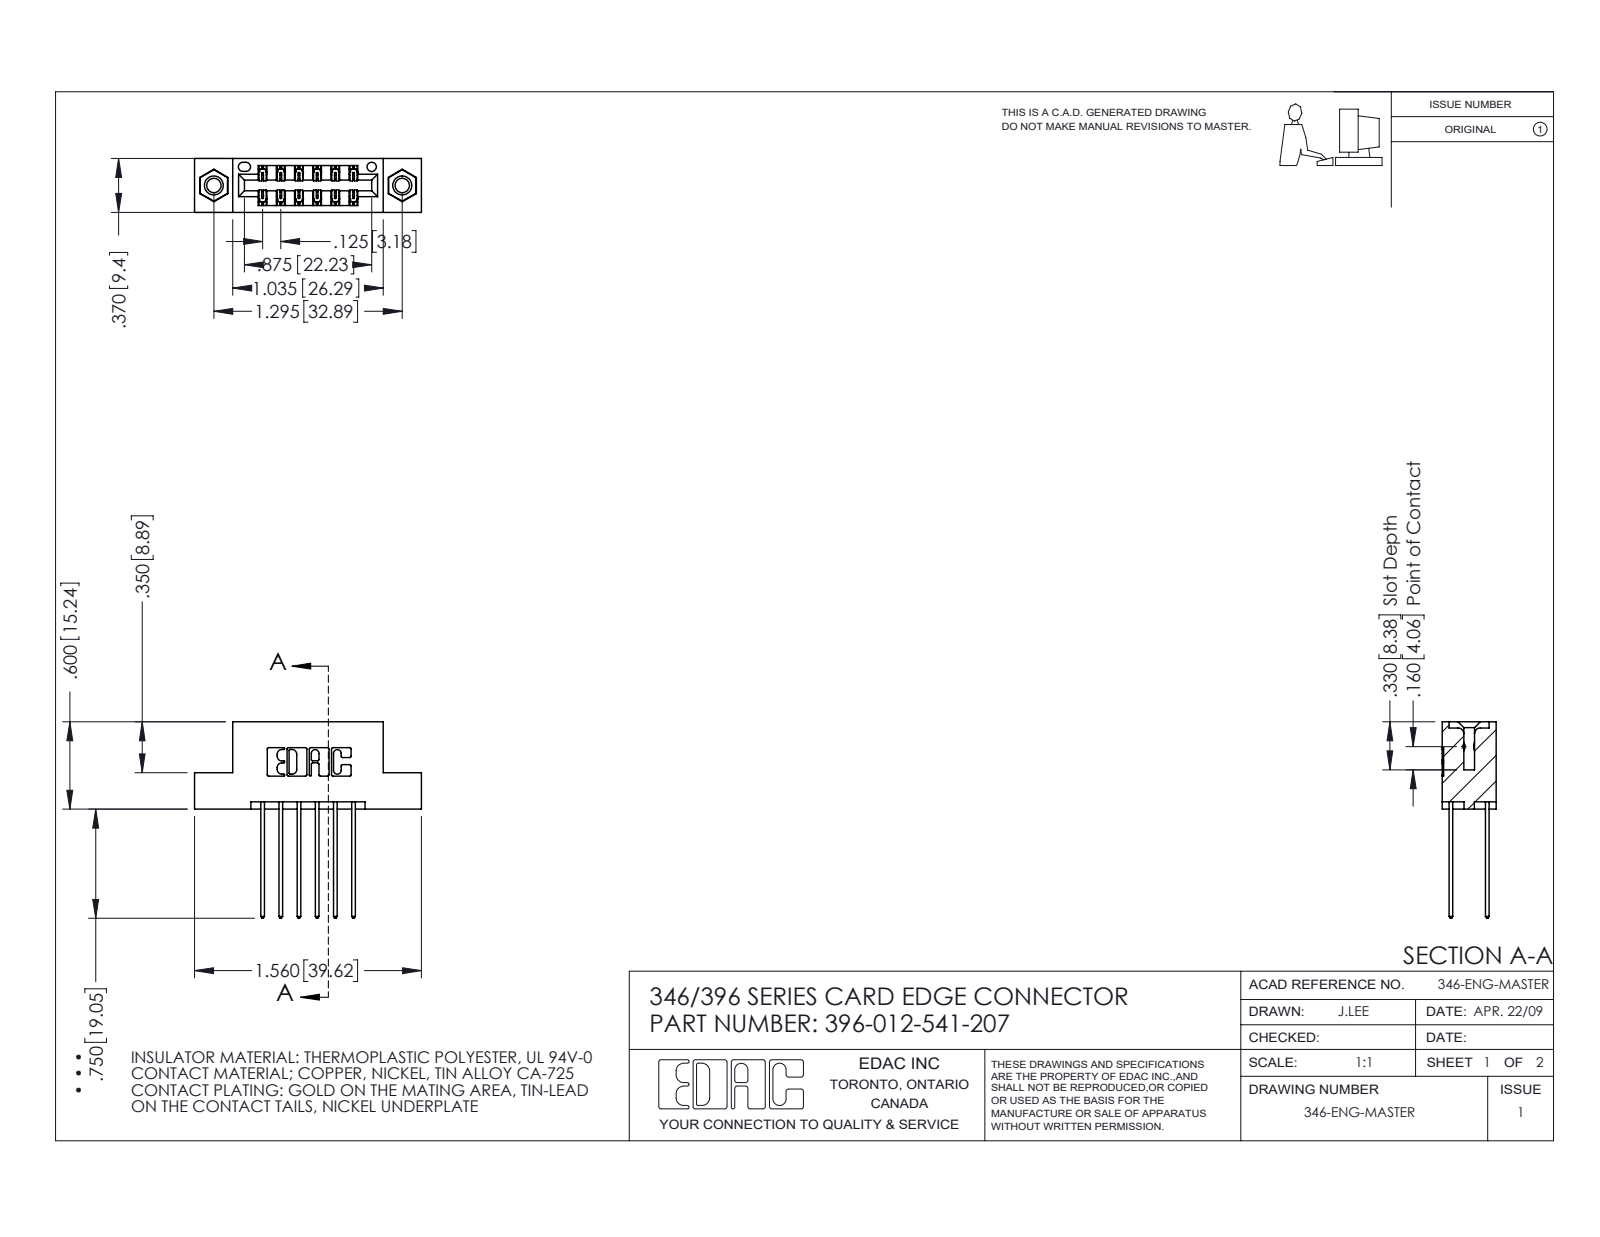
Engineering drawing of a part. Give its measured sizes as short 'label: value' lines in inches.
name: 345-292-001_345-293-141; 345-250-001_345-250-005-103; 396-012-541-207; 346 Part_Flush Mounting Lugs - 0.156 Dia-TI
written by: SolidWorks 2016 (CONFIG_CONTROL_DESIGN)
unit: in
bodies: 15 solids, 806 faces (528 planar, 262 cylindrical, 16 other)
size: 1.56 × 1.35 × 0.37
volume: 0.222 in³; area: 7.441 in²
holes: 2× ⌀0.098, 2× ⌀0.125, 2× ⌀0.156, 1× ⌀0.064
bosses: 2× ⌀0.155
rounds: 22× R0.01, 18× R0.006, 12× R0.01, 6× R0.007, 6× R0.031, 3× R0.026, 2× R0.014, 2× R0.022
face distances: 0.25, 0.048, 0.322, 0.37, 0.025, 0.072, 0.298, 0.275, 0.148, 0.222
hole spacings: 0.246, 1.092, 1.295
